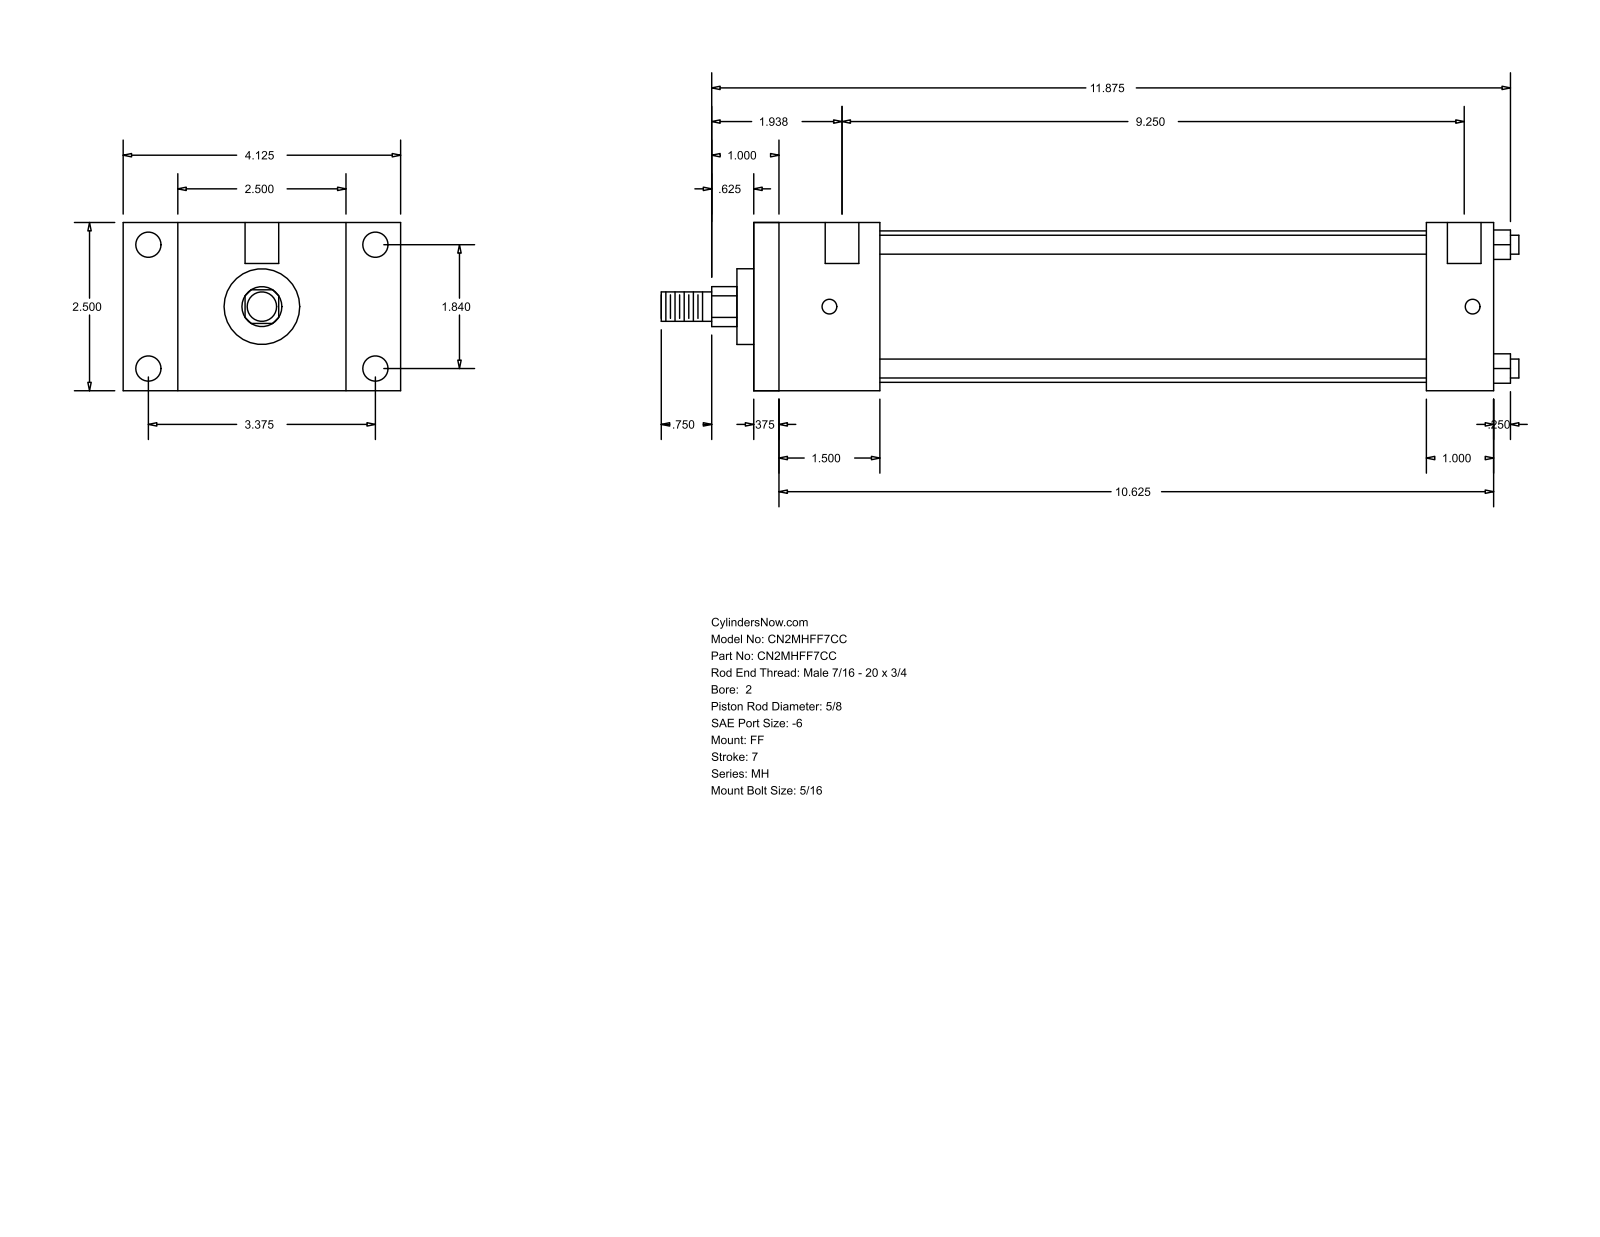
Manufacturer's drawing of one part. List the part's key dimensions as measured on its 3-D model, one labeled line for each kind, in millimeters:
Part name (STEP PRODUCT): MH_FF__0200_0.625
STEP written by: GSSL Pune (CONFIG_CONTROL_DESIGN)
Units: millimetres
Bodies: 0 solids, 92 faces (64 planar, 28 cylindrical, 0 other)
Overall size (bounding box): 323.85 × 104.78 × 63.5
Round holes (diameter × count): ⌀5.56 ×4, ⌀9.53 ×4, ⌀12.7 ×2
Round bosses / shafts (diameter × count): ⌀7.14 ×4, ⌀57.15 ×1, ⌀28.57 ×1, ⌀15.88 ×1, ⌀11.11 ×1
Partial cylindrical surfaces — rounded edges, fillets, slot ends (radius × count): R7.54 ×1
Main face-to-face distances: 63.5, 279.39, 9.52, 269.87, 38.1, 47.62, 254, 244.48, 206.38, 231.77
Hole centre spacings: 46.74, 85.72, 97.63, 242.89, 3.18, 4.76, 234.95, 238.13
